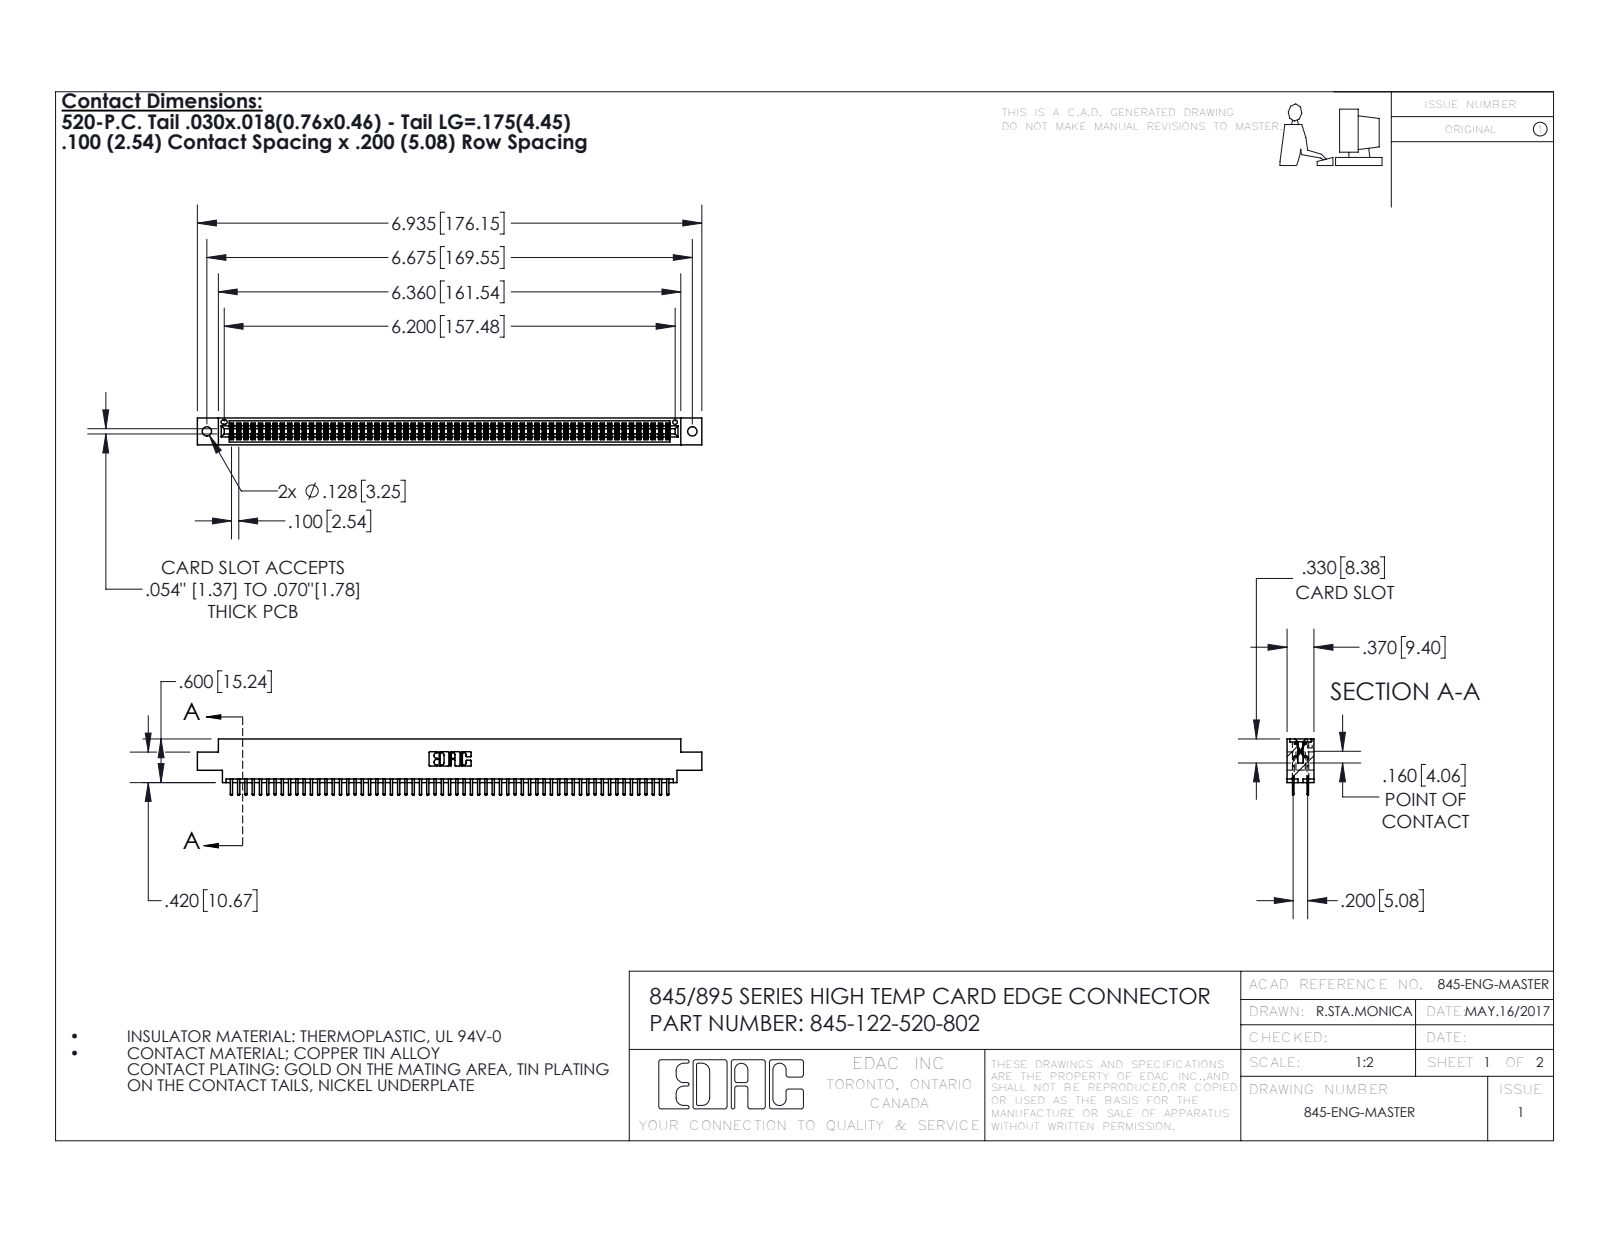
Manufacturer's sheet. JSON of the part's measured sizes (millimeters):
{"part_name": "845 Part_0.170 Offset - 0.128 Dia; 345-292-001_345-293-120; 845-122-520-802", "step_written_by": "SolidWorks 2016 (CONFIG_CONTROL_DESIGN)", "units": "millimeters", "bodies": {"solids": 123, "faces": 6718, "planar": 4354, "cylindrical": 2364, "other": 0}, "overall_size": [176.1, 19.7, 9.4], "volume_mm3": 17090, "surface_area_mm2": 25380, "round_holes": [[3.3, 2], [1.6, 1]], "partial_cylinders_radius": [[0.2, 183], [0.3, 126], [0.3, 22], [0.2, 6], [0.8, 6], [0.7, 3], [0.4, 2], [0.5, 2]], "face_to_face_distances": [1.8, 7.6, 5.1, 9.4, 2.5, 6.9, 0.6, 5.7, 0.6, 1.8], "hole_center_spacings": [6.9, 163.6, 169.5]}
